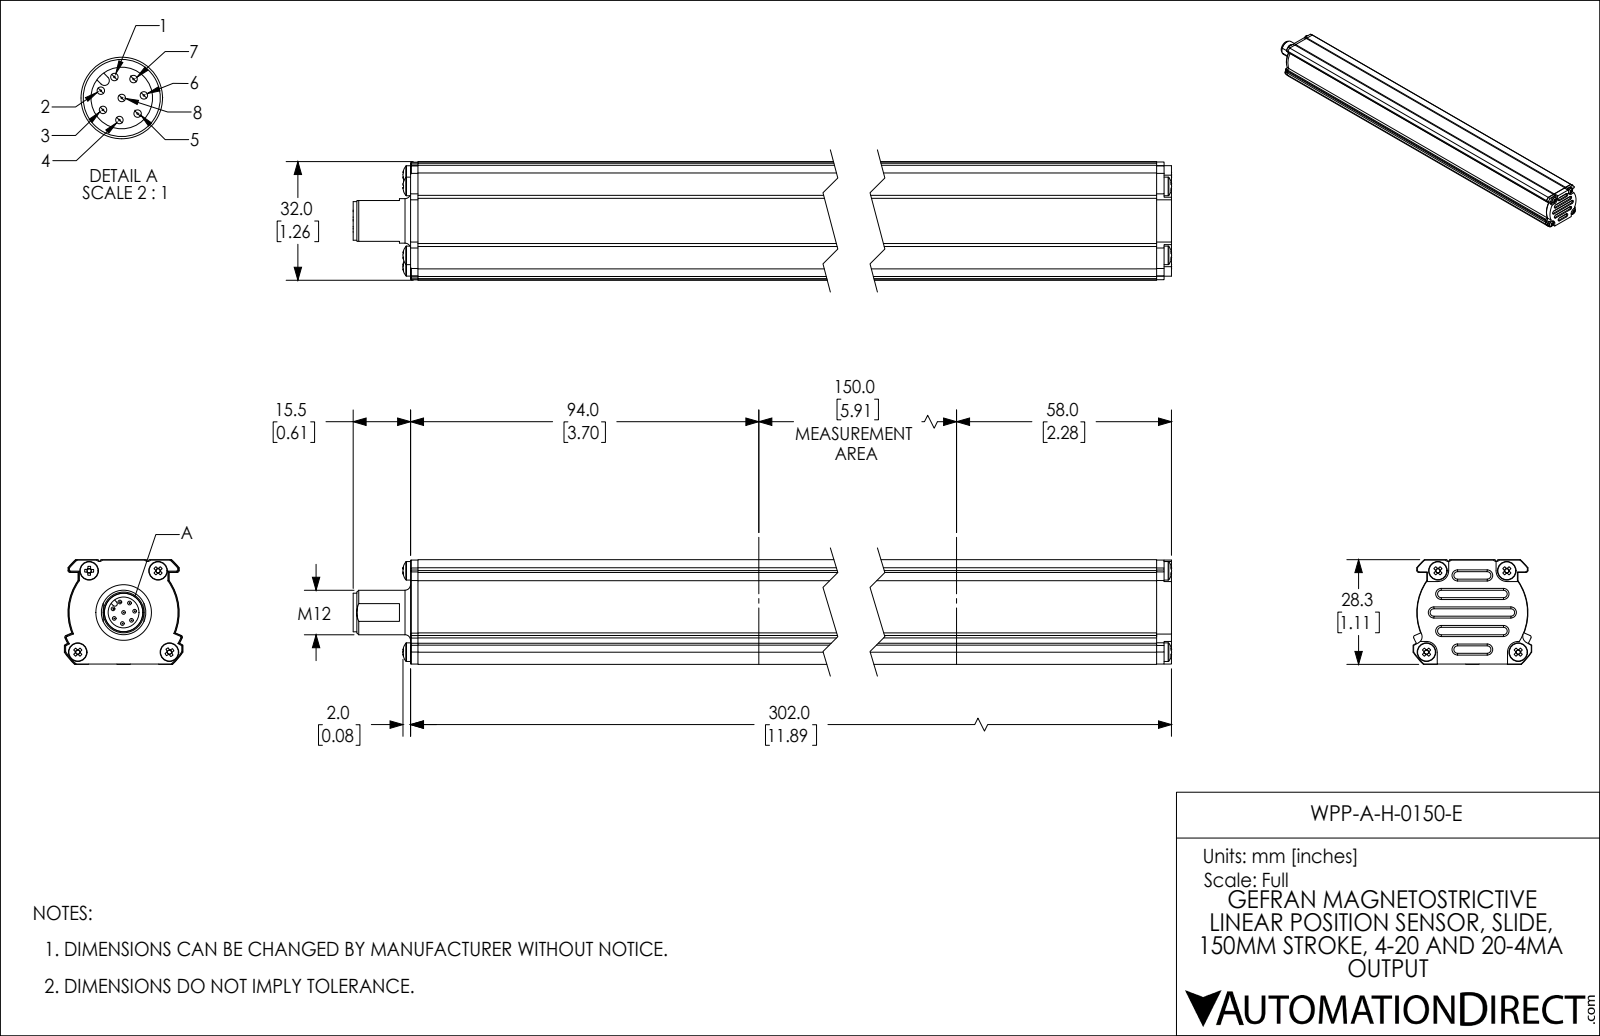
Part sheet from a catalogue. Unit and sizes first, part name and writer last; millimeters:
Units: millimetres
Overall size (bounding box): 317.6 × 32 × 28.2
Round holes (diameter × count): ⌀2.3 ×4, ⌀2.6 ×4, ⌀7 ×1, ⌀8.3 ×1, ⌀9.4 ×1
Round bosses / shafts (diameter × count): ⌀1 ×8, ⌀5 ×4, ⌀12 ×1, ⌀10.4 ×1, ⌀9.6 ×1, ⌀8 ×1
Partial cylindrical surfaces — rounded edges, fillets, slot ends (radius × count): R0.5 ×8, R2.9 ×4, R0.4 ×2, R1 ×2, R1.9 ×2, R0.7 ×1, R2 ×1, R14.9 ×1
Main face-to-face distances: 28, 28.2, 296, 24.8, 24.6, 3.5, 3.7, 28.3, 2, 298
Hole centre spacings: 14.6, 16.4, 18.6, 22.1, 22.2, 24.7, 30.8, 30.9
Volume: 241 400 mm³ · Surface area: 53 610 mm²
Bodies: 20 solids, 573 faces (301 planar, 131 cylindrical, 141 other)
Part name (STEP PRODUCT): WPP-A-H-0150-E
STEP written by: SolidWorks 2021 (CONFIG_CONTROL_DESIGN)
